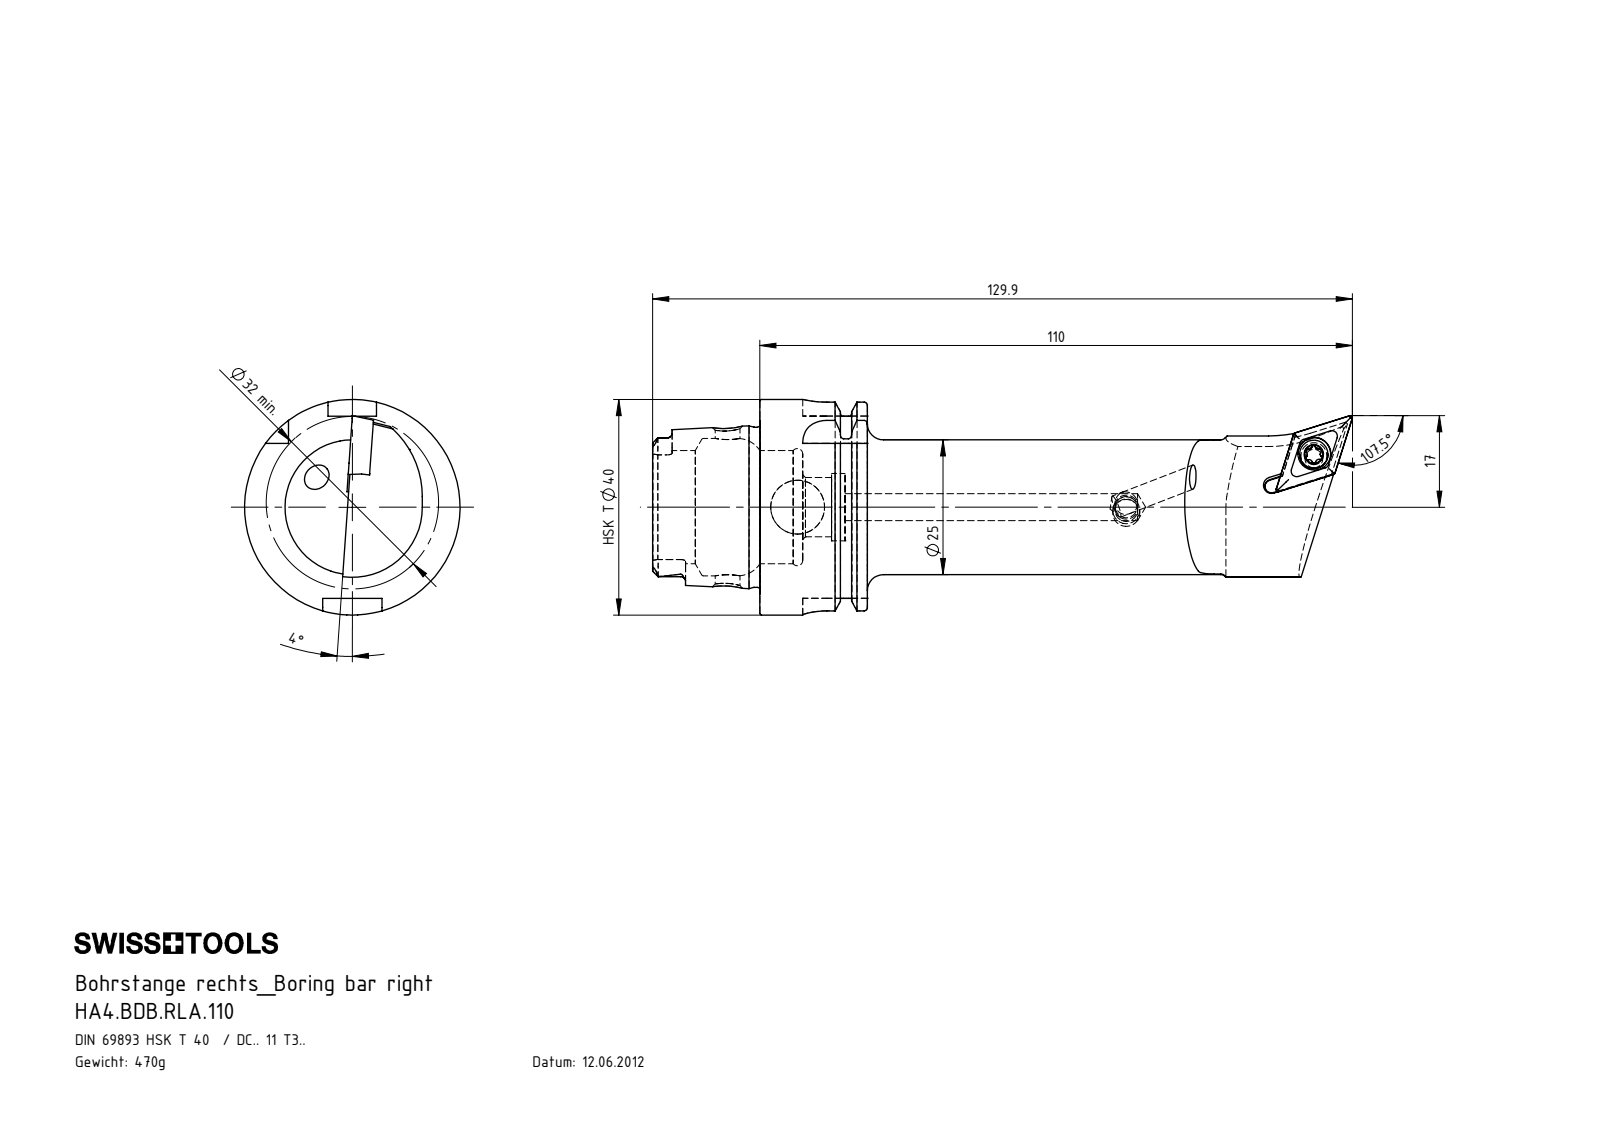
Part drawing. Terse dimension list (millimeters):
name: HA4.BDB.RLA.110; KVT_MB_600_050; HA4-BDB.RLA.110_A; WCB-ER2.001.009_A (+1 more)
written by: SolidWorks 2017 (AUTOMOTIVE_DESIGN)
unit: mm
bodies: 5 solids, 310 faces (77 planar, 90 cylindrical, 143 other)
size: 129.9 × 40 × 40
volume: 59 649 mm³; area: 17 974 mm²
holes: 2× ⌀4.2, 2× ⌀5, 1× ⌀3.3, 1× ⌀4, 1× ⌀4.4, 1× ⌀4.6, 1× ⌀6.1, 1× ⌀10, 1× ⌀11, 1× ⌀12.5, 1× ⌀21, 1× ⌀25.5
bosses: 1× ⌀40, 1× ⌀34.75, 1× ⌀29.71, 1× ⌀25, 1× ⌀5.25, 1× ⌀5, 1× ⌀4
rounds: 6× R0.34, 6× R0.59, 6× R0.9, 4× R1.88, 4× R4.5, 1× R1.25, 1× R3, 1× R13
face distances: 19.95, 7.95, 12, 3.66, 19.9, 27.85, 39.85, 35.7, 15.8, 7.85
